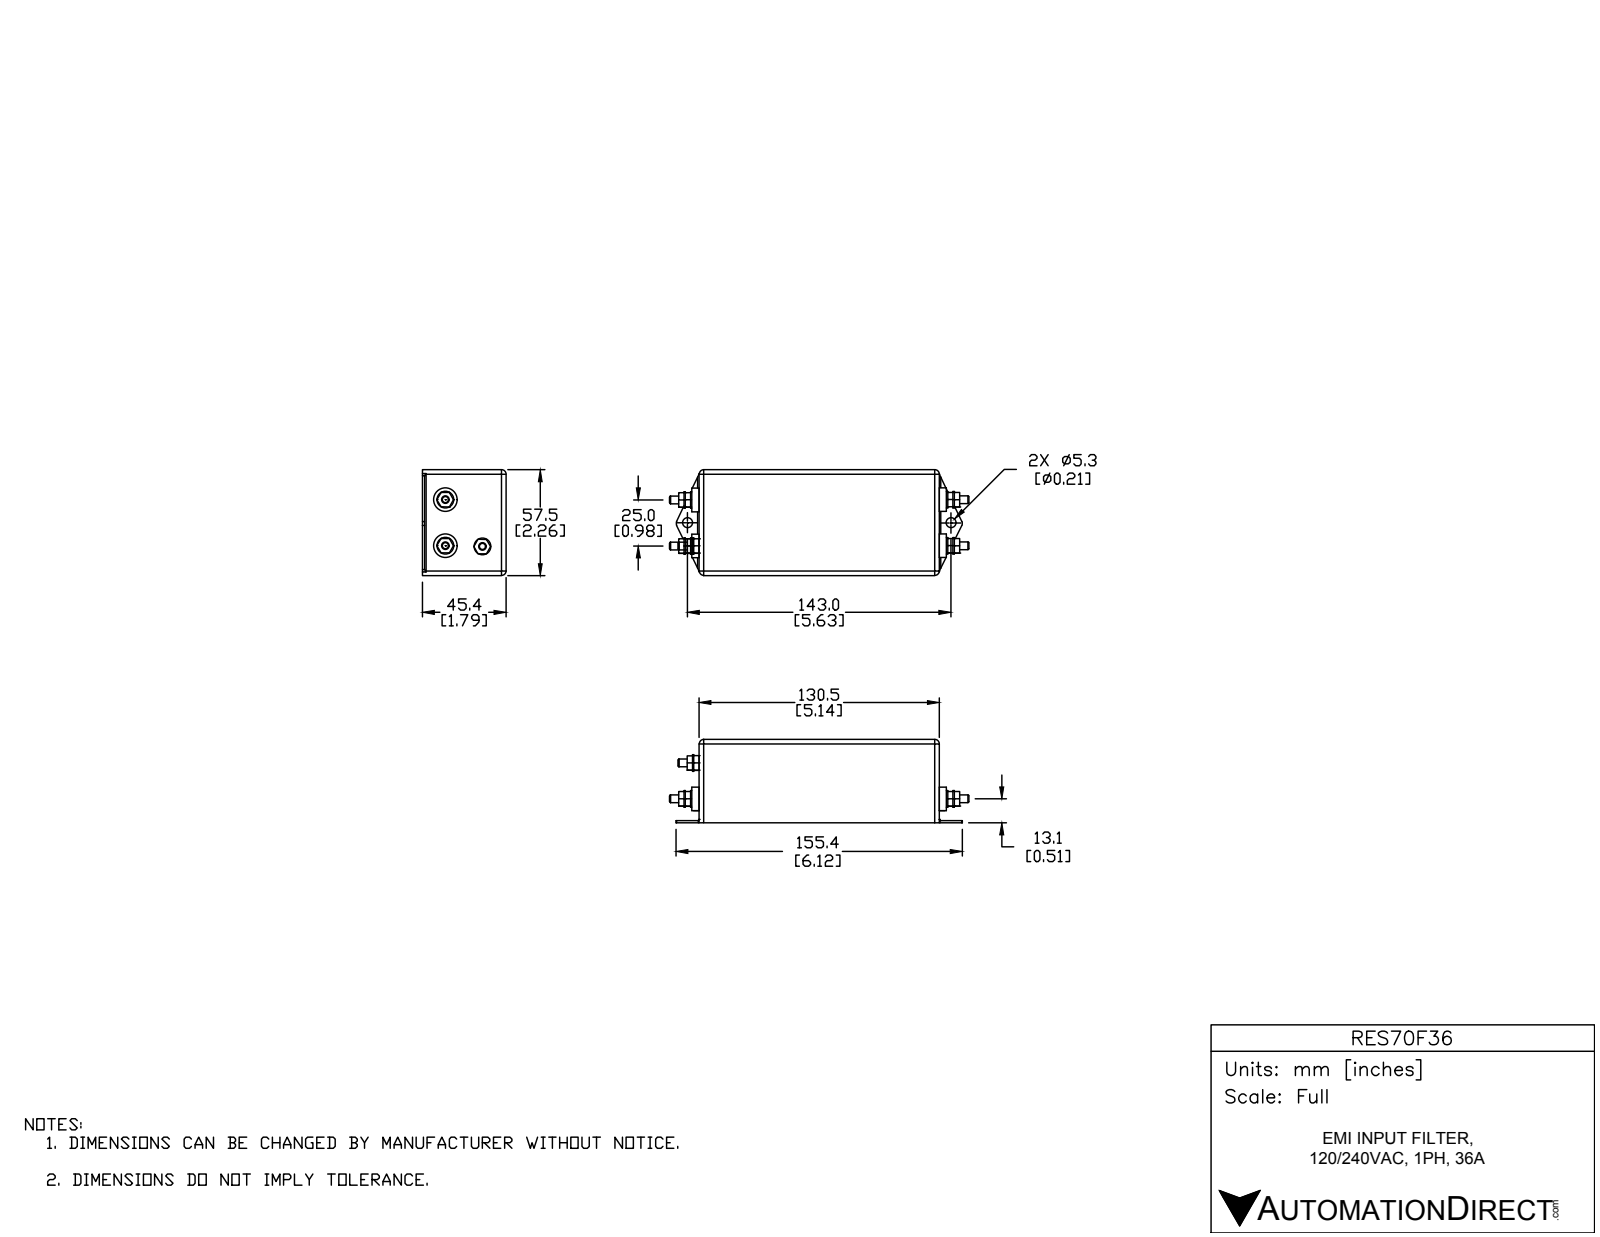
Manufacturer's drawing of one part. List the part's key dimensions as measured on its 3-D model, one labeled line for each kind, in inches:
Part name (STEP PRODUCT): RES70S36
STEP written by: SolidWorks 2015 (AUTOMOTIVE_DESIGN)
Units: inches
Bodies: 1 solid, 52 faces (17 planar, 29 cylindrical, 6 other)
Overall size (bounding box): 6.122 × 2.264 × 1.787
Volume: 21.32 in³ · Surface area: 51.39 in²
Round holes (diameter × count): ⌀0.209 ×2, ⌀0.079 ×1
Round bosses / shafts (diameter × count): ⌀0.504 ×2
Partial cylindrical surfaces — rounded edges, fillets, slot ends (radius × count): R0.197 ×12, R0.098 ×2, R0.03 ×1
Main face-to-face distances: 1.787, 2.264, 5.276, 0.15, 5.425, 0.047, 1.74, 5.575, 5.421, 5.272
Hole centre spacings: 5.63
